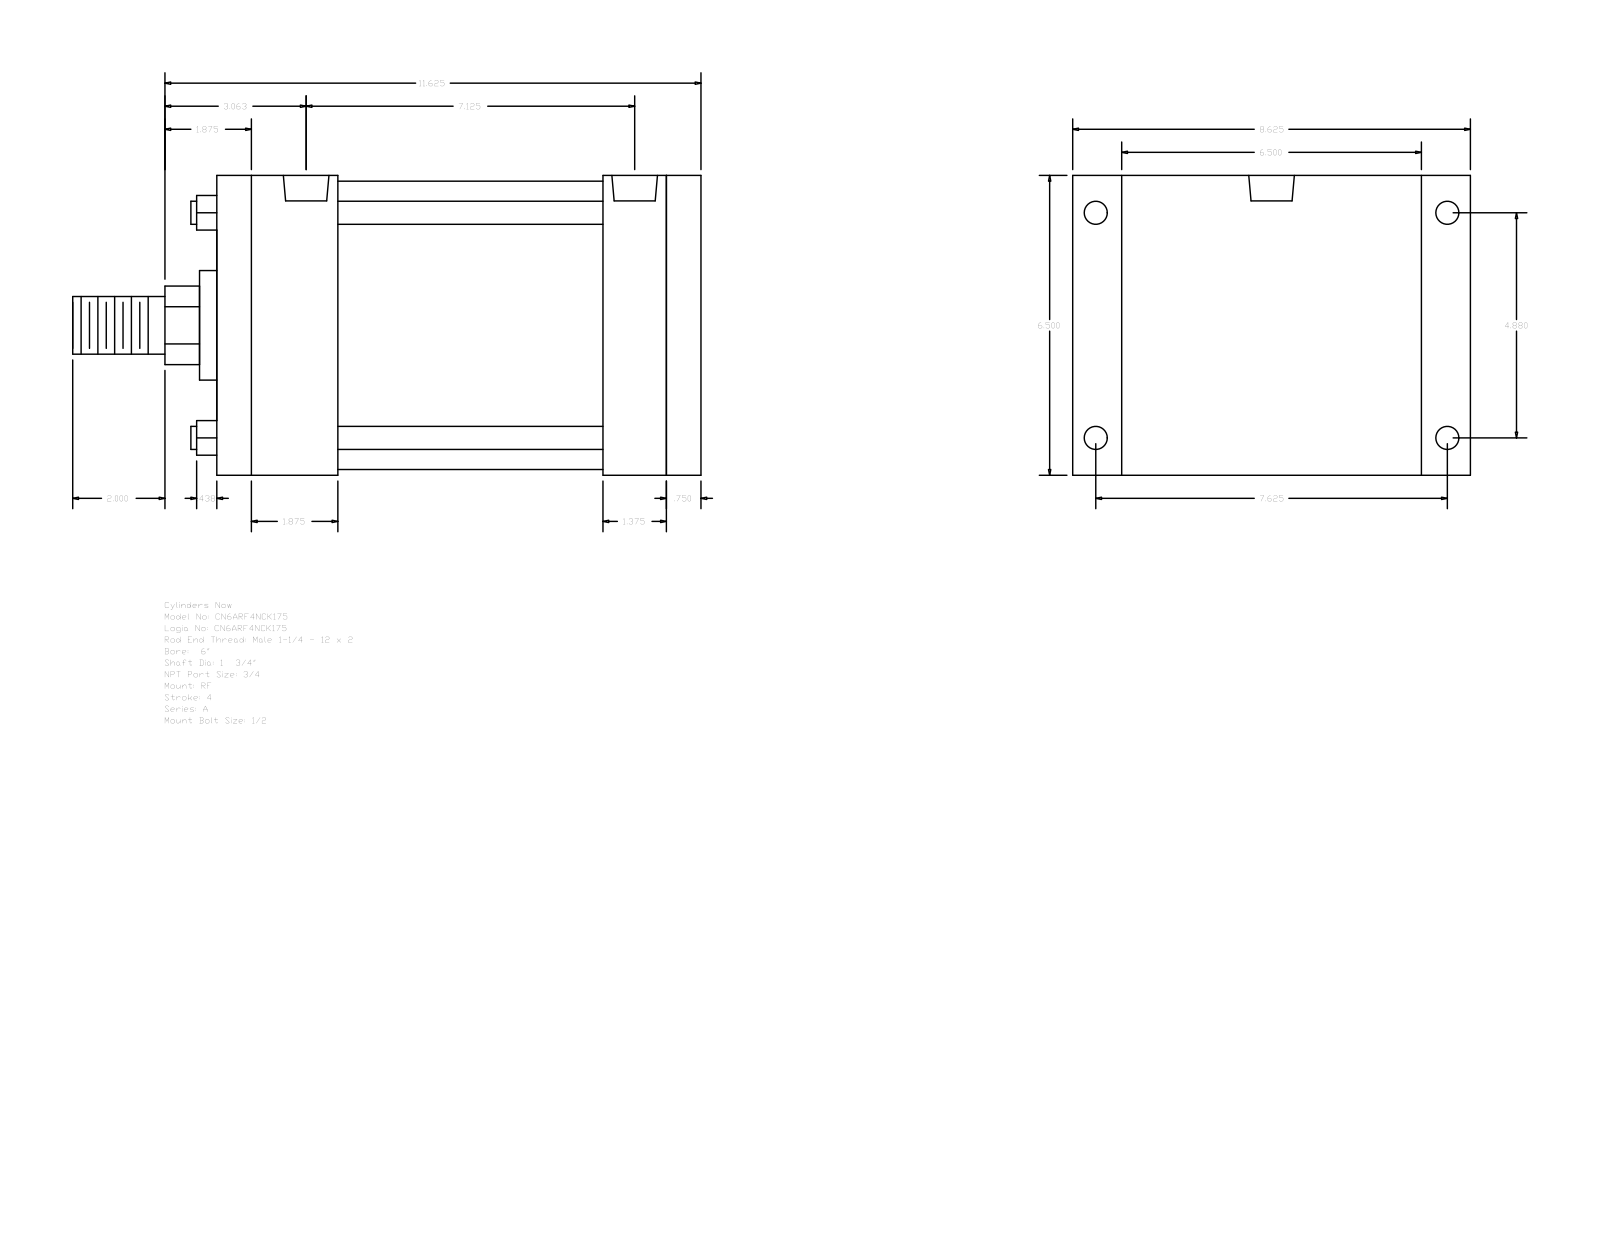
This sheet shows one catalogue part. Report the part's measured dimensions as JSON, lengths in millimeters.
{"part_name": "A_RF__0600_1.75", "step_written_by": "GSSL Pune (CONFIG_CONTROL_DESIGN)", "units": "millimeters", "bodies": {"solids": 0, "faces": 92, "planar": 64, "cylindrical": 28, "other": 0}, "overall_size": [346.07, 219.07, 165.1], "round_holes": [[12.7, 4], [15.08, 4], [25.12, 2]], "round_bosses_or_shafts": [[12.7, 4], [158.75, 1], [60.33, 1], [44.45, 1], [31.75, 1]], "partial_cylinders_radius": [[21.63, 1]], "face_to_face_distances": [165.1, 266.7, 247.66, 19.04, 146.05, 66.68, 180.98, 200.02, 212.73, 34.93], "hole_center_spacings": [5.56, 123.96, 169.85, 175.41, 193.68, 229.95, 180.97]}
